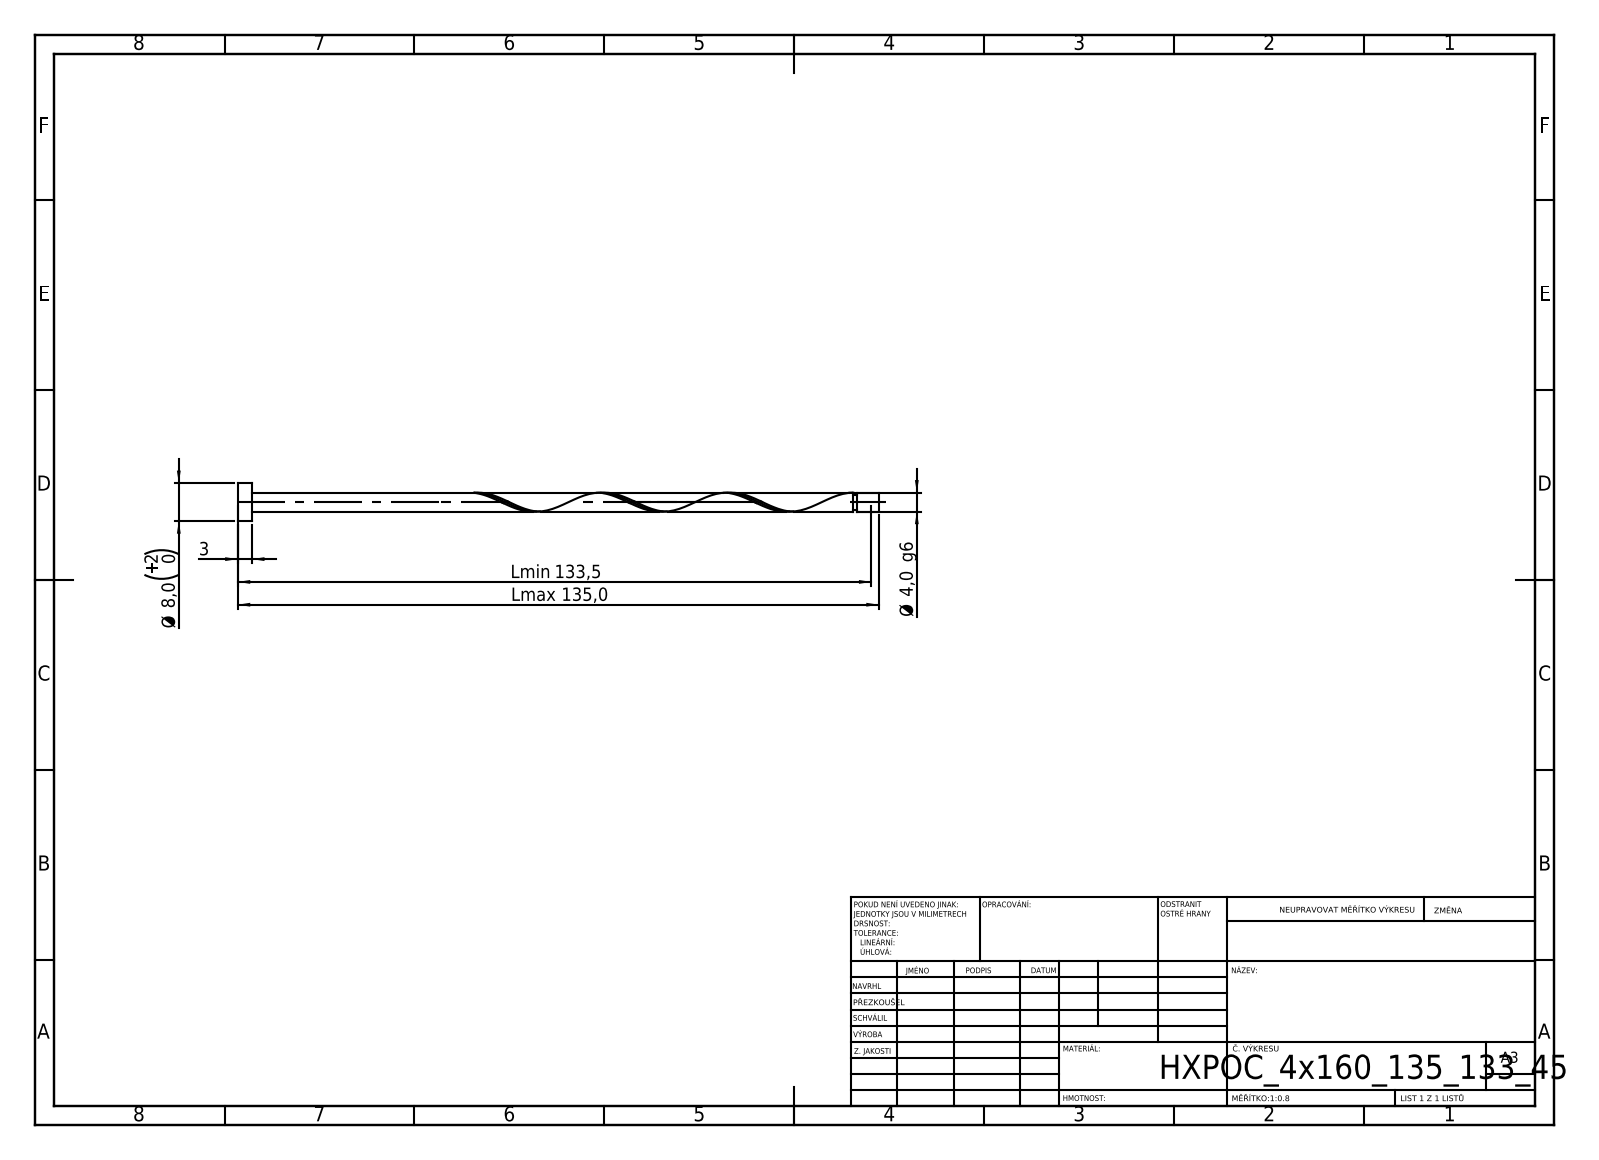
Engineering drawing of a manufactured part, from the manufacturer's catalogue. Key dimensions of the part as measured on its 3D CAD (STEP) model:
STEP written by: SolidWorks 2019 (CONFIG_CONTROL_DESIGN)
Units: millimetres
Bodies: 1 solid, 21 faces (6 planar, 14 cylindrical, 1 other)
Overall size (bounding box): 135 × 8 × 8
Volume: 1 787 mm³ · Surface area: 1 876 mm²
Round bosses / shafts (diameter × count): ⌀8 ×1, ⌀4 ×1, ⌀3.2 ×1
Main face-to-face distances: 3, 135, 132, 130.46, 127.46, 4.54, 129.66, 126.66, 0.8, 5.34
